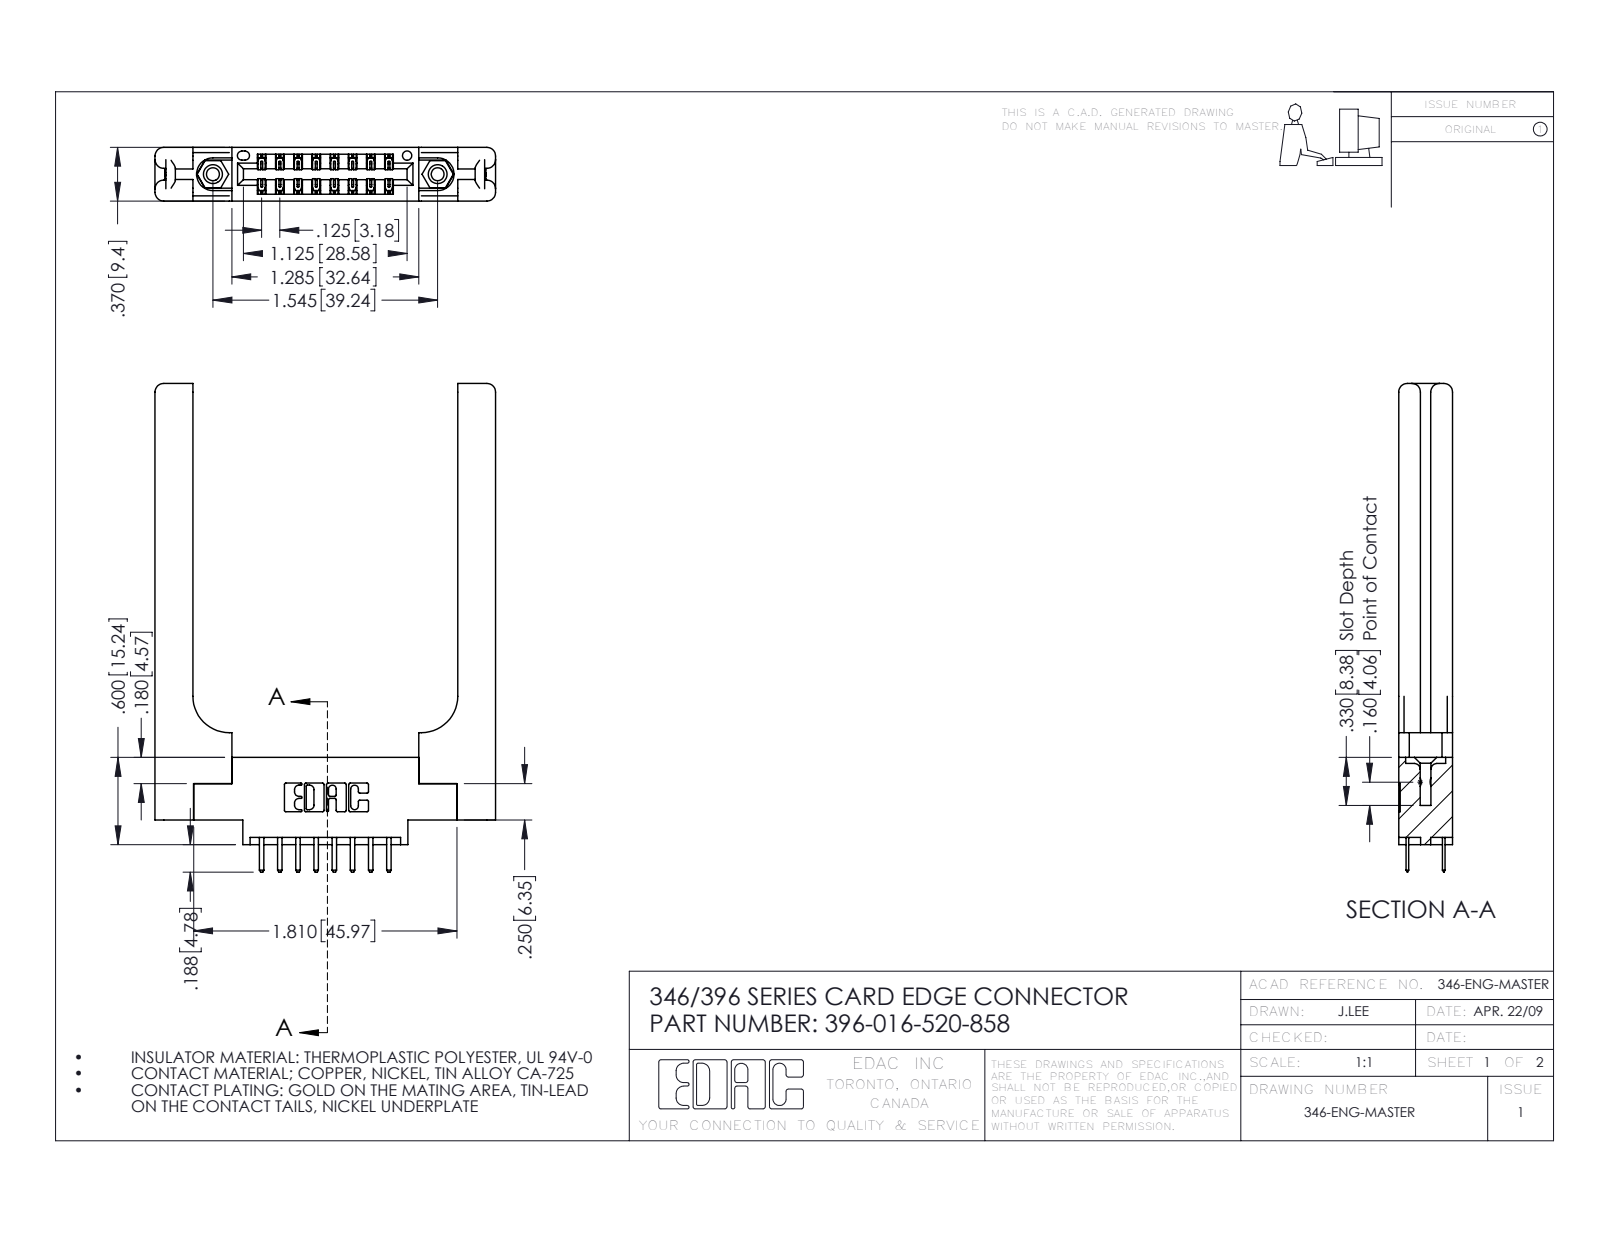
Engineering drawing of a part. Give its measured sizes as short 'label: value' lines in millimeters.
name: 345-292-001_345-293-120; 396-016-520-858; 346 Part_0.170 Offset - 0.156 Dia-TH; 346-220-058_345-220-058 (+1 more)
written by: SolidWorks 2016 (CONFIG_CONTROL_DESIGN)
unit: mm
bodies: 21 solids, 1278 faces (820 planar, 398 cylindrical, 60 other)
size: 85.3 × 59.5 × 9.4
volume: 12 900 mm³; area: 11 990 mm²
holes: 2× ⌀2.3, 2× ⌀3.2, 2× ⌀4, 1× ⌀1.6
bosses: 2× ⌀3.9
rounds: 24× R0.2, 22× R0.3, 20× R0.3, 16× R1.5, 6× R0.2, 6× R0.8, 3× R0.7, 2× R0.4
face distances: 9.4, 3.8, 5.6, 1.8, 6.4, 3.8, 2.6, 1.2, 8.2, 4.4
hole spacings: 6.2, 34.1, 39.2
